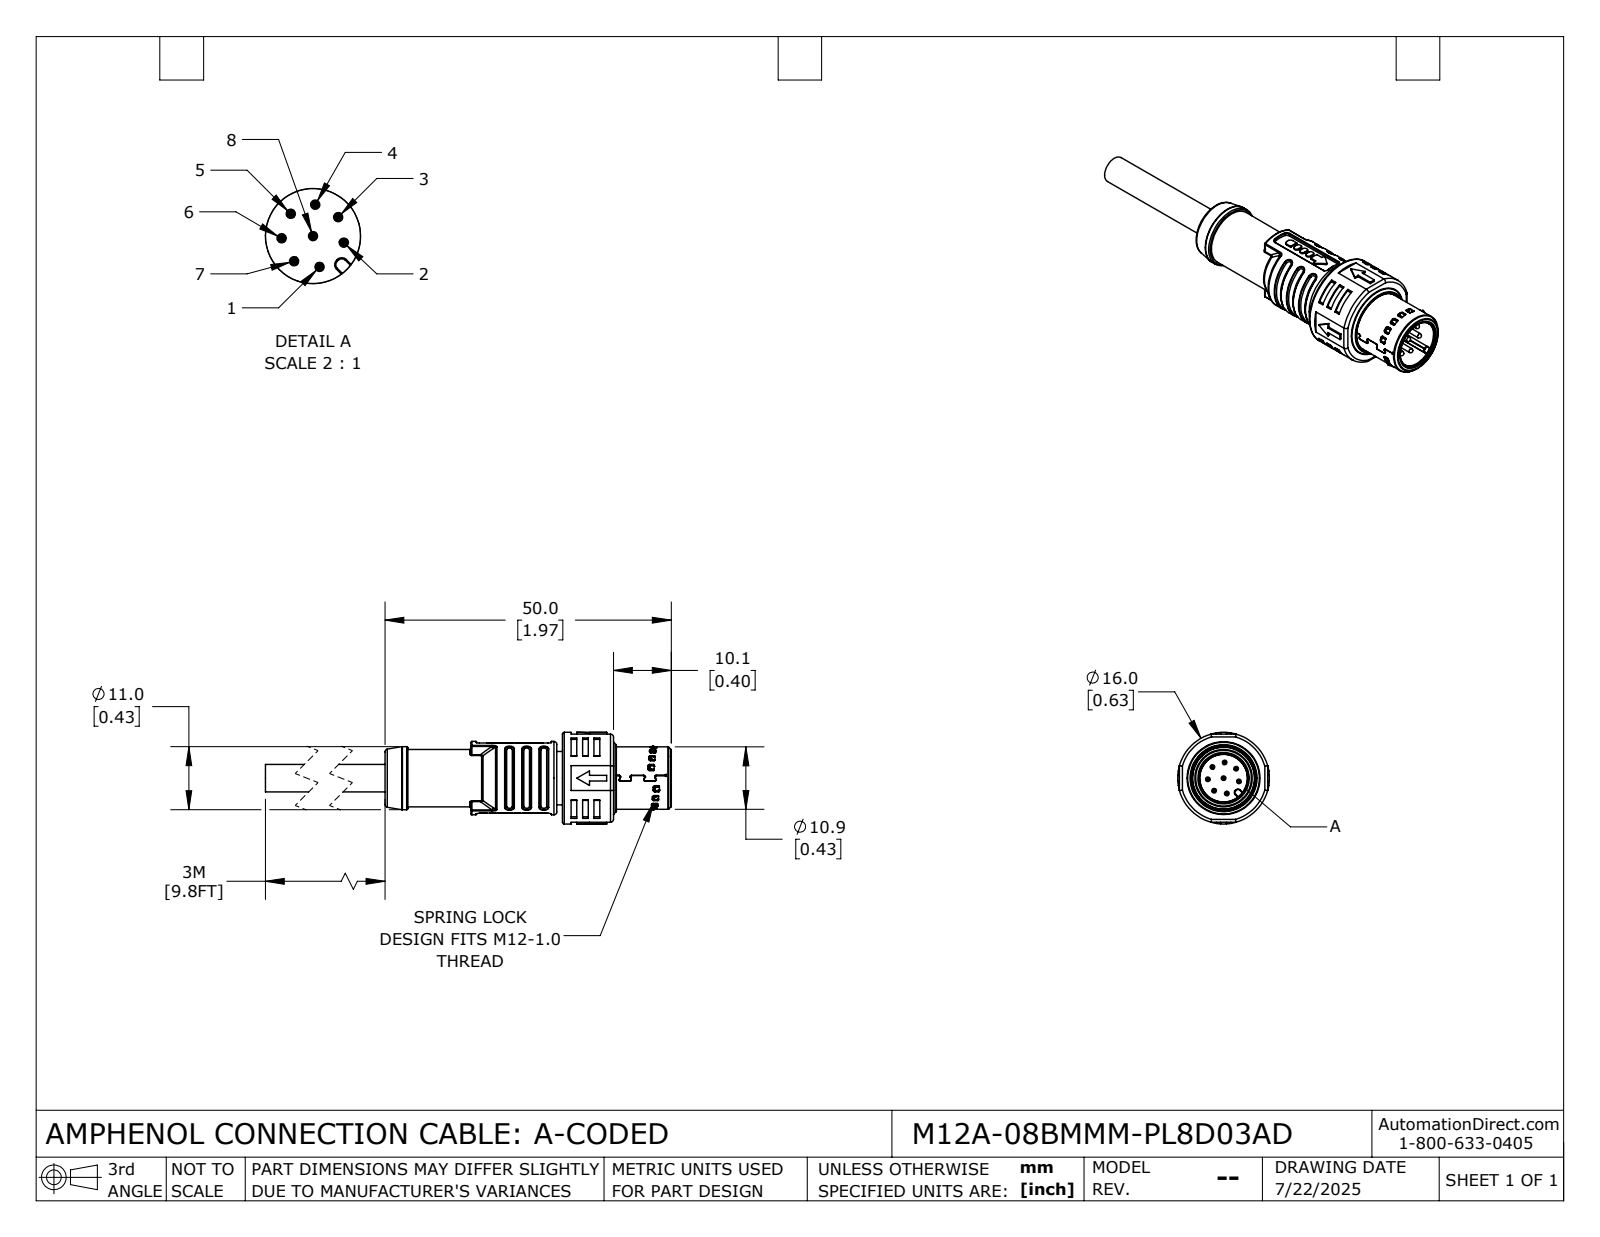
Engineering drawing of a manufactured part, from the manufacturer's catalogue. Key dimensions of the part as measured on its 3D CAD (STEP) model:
Part name (STEP PRODUCT): M12A-08BMMM-PL8D03AD
STEP written by: SolidWorks 2024 (CONFIG_CONTROL_DESIGN)
Units: millimetres
Bodies: 1 solid, 2027 faces (880 planar, 644 cylindrical, 503 other)
Overall size (bounding box): 75 × 16 × 16
Volume: 5 223 mm³ · Surface area: 5 723 mm²
Round holes (diameter × count): ⌀8.3 ×1, ⌀9 ×1, ⌀10.15 ×1, ⌀10.5 ×1, ⌀10.9 ×1, ⌀11.5 ×1, ⌀11.8 ×1, ⌀14.2 ×1
Round bosses / shafts (diameter × count): ⌀0.8 ×8, ⌀16 ×1, ⌀14.1 ×1, ⌀12.8 ×1, ⌀12.4 ×1, ⌀11 ×1, ⌀10.45 ×1, ⌀10.4 ×1
Partial cylindrical surfaces — rounded edges, fillets, slot ends (radius × count): R0.2 ×114, R0.25 ×66, R0.3 ×64, R0.15 ×44, R0.5 ×38, R0.13 ×12, R0.7 ×11, R0.1 ×10
Main face-to-face distances: 1, 10.1, 8.6, 8.9, 2.5, 1.5, 1.2, 32.5, 15.4, 41.1
